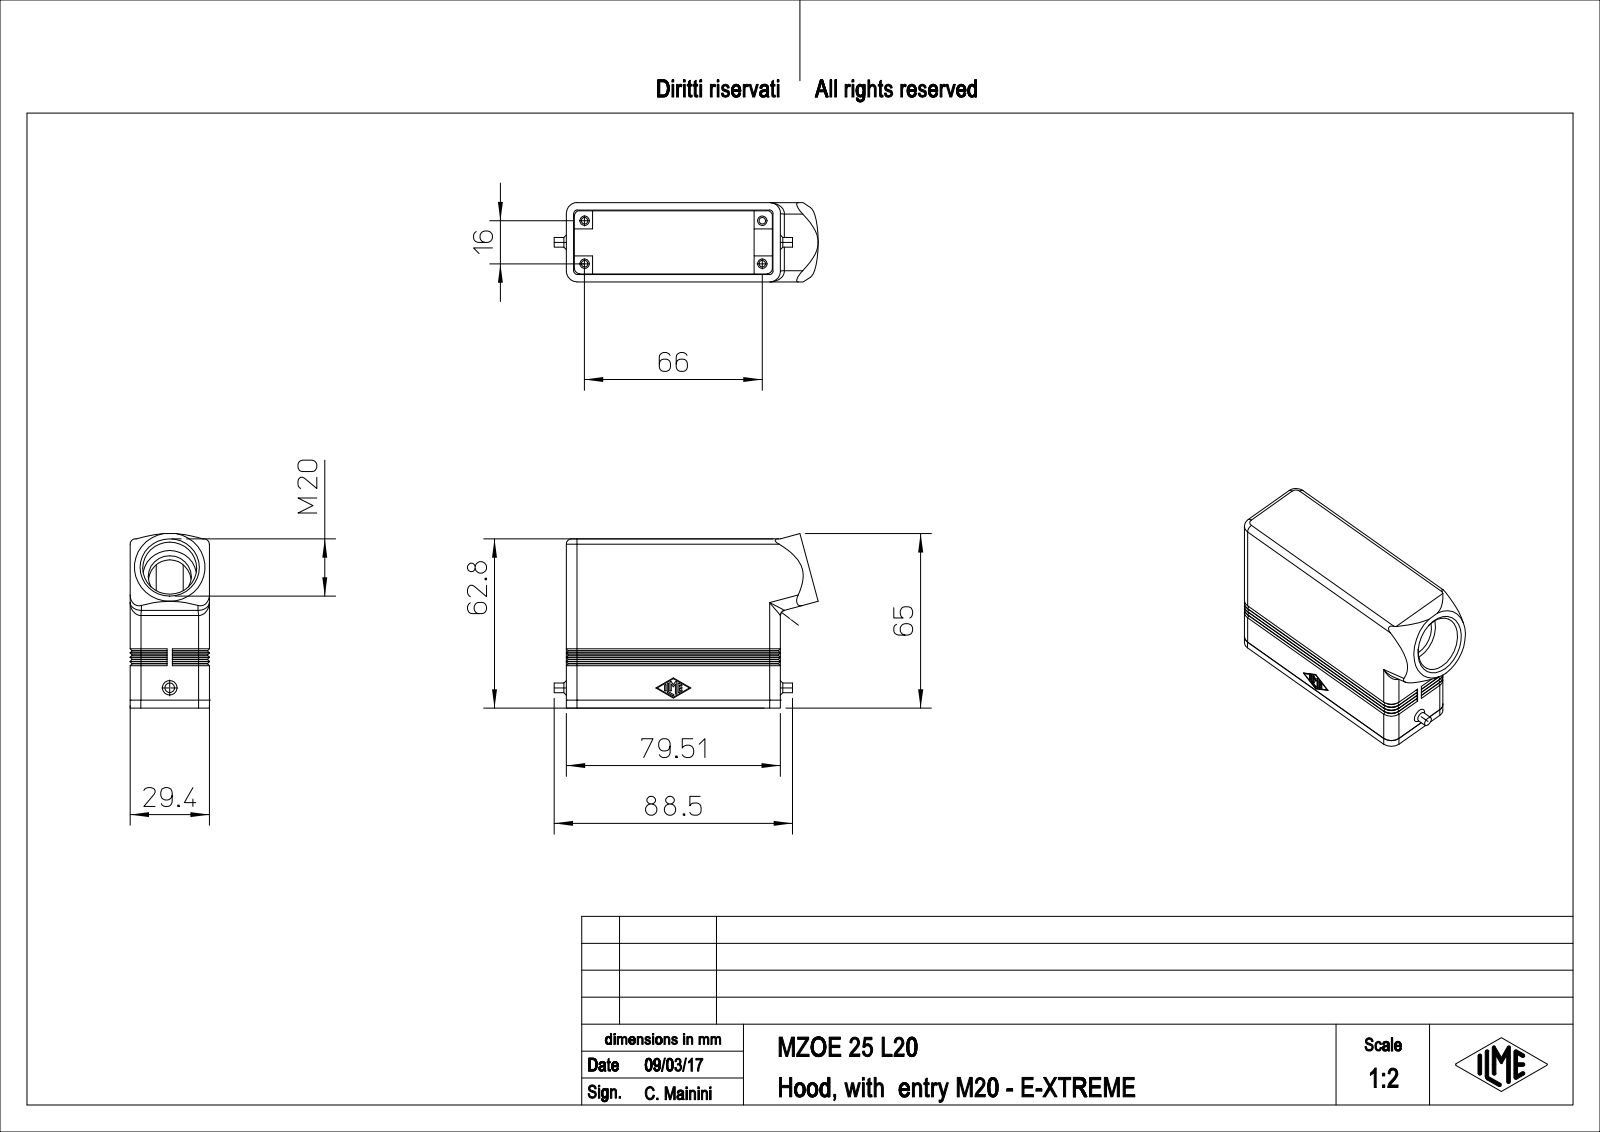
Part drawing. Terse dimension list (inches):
name: MZOE_25_L20
written by: PTC Creo Elements/Direct Modeling 19.0E 27-Jun-2016 (C) Parametric Technology GmbH (AUTOMOTIVE_DESIGN)
unit: in
bodies: 1 solid, 320 faces (176 planar, 91 cylindrical, 53 other)
size: 3.859 × 2.549 × 1.158
volume: 3.317 in³; area: 48.97 in²
holes: 4× ⌀0.097, 4× ⌀0.138, 1× ⌀0.63, 1× ⌀0.787
bosses: 1× ⌀0.142
rounds: 14× R0.01, 8× R0.157, 7× R0.079, 4× R0.049, 4× R0.13, 2× R0.165
face distances: 0.118, 1.039, 1.157, 0.921, 2.746, 0.384, 2.628, 0.266, 3.012, 0.044
hole spacings: 0.63, 2.598, 2.674
